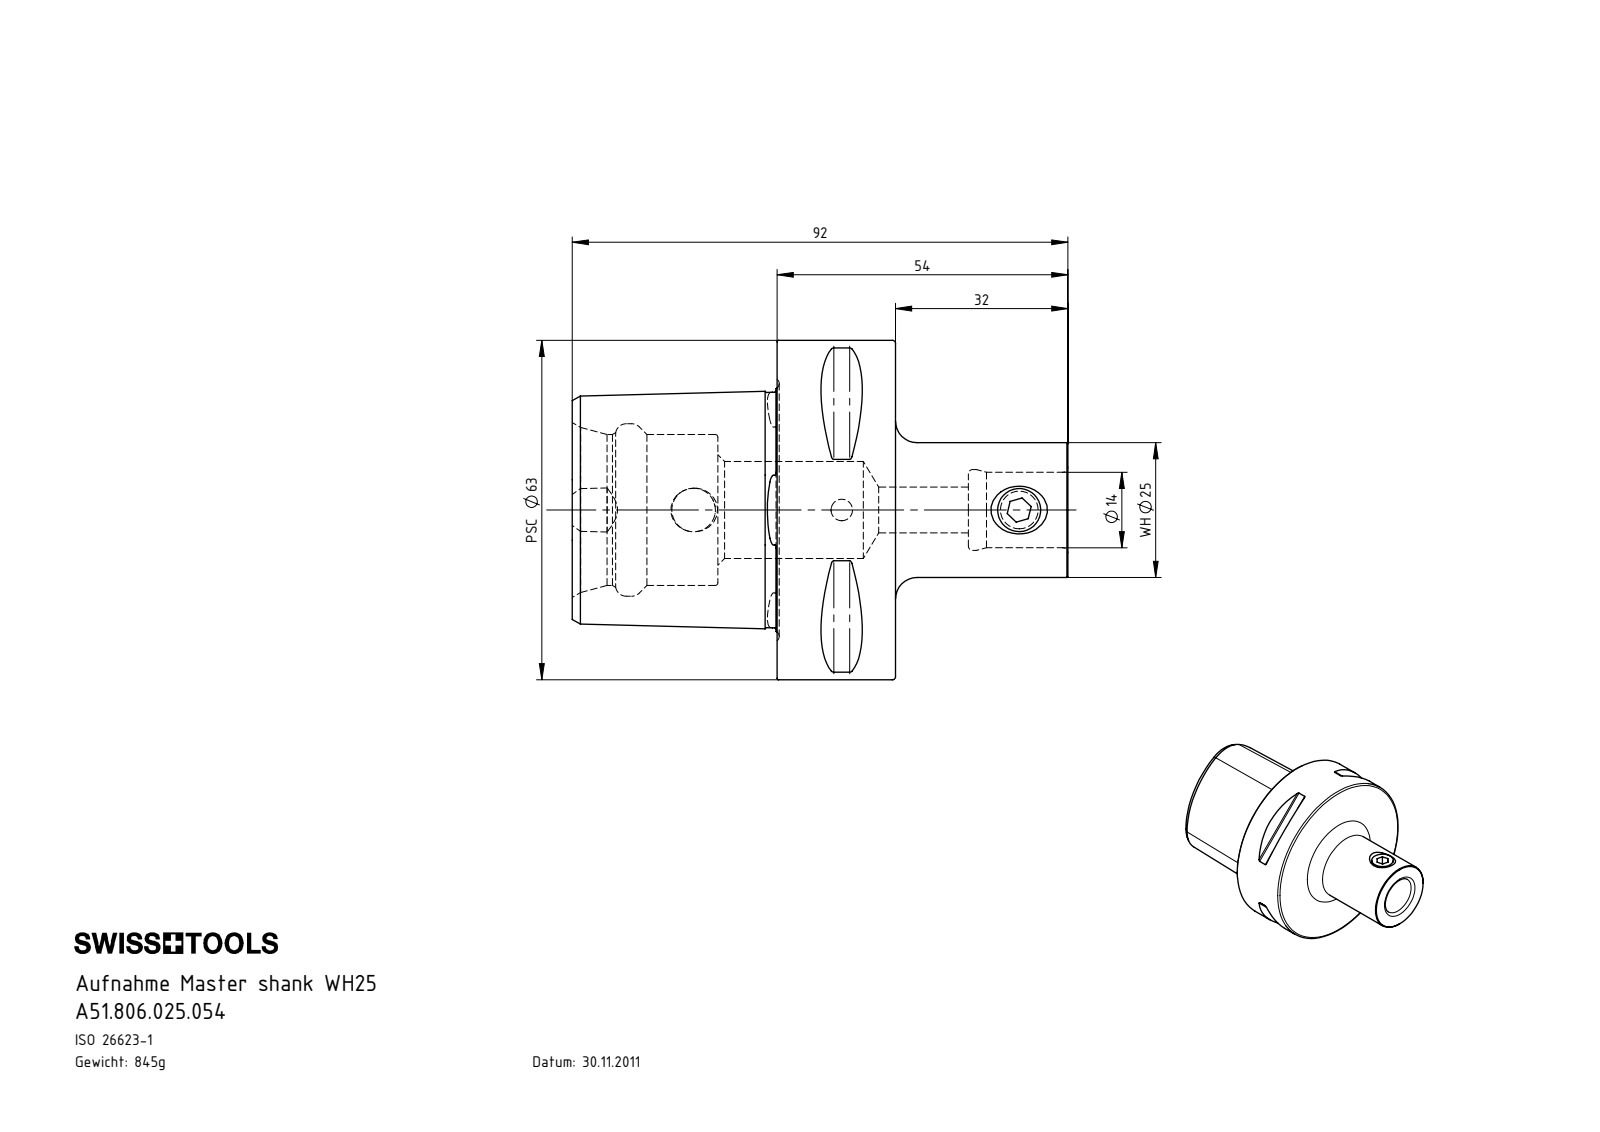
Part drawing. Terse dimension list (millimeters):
name: A51.806.025.054; WH2-ER1.001.010; PS6-WH2.K01.054_B
written by: SolidWorks 2022 (AUTOMOTIVE_DESIGN)
unit: mm
bodies: 2 solids, 158 faces (30 planar, 37 cylindrical, 91 other)
size: 92 × 63 × 63
volume: 107 916 mm³; area: 23 894 mm²
holes: 1× ⌀4, 1× ⌀7, 1× ⌀8.1, 1× ⌀8.5, 1× ⌀14, 1× ⌀15, 1× ⌀18, 1× ⌀28, 1× ⌀32
bosses: 1× ⌀63, 1× ⌀25, 1× ⌀8
rounds: 8× R0.5, 1× R6
face distances: 22, 38, 60, 24.88, 92, 54, 32, 27, 11, 33
hole spacings: 27.5, 32.95, 60.45
